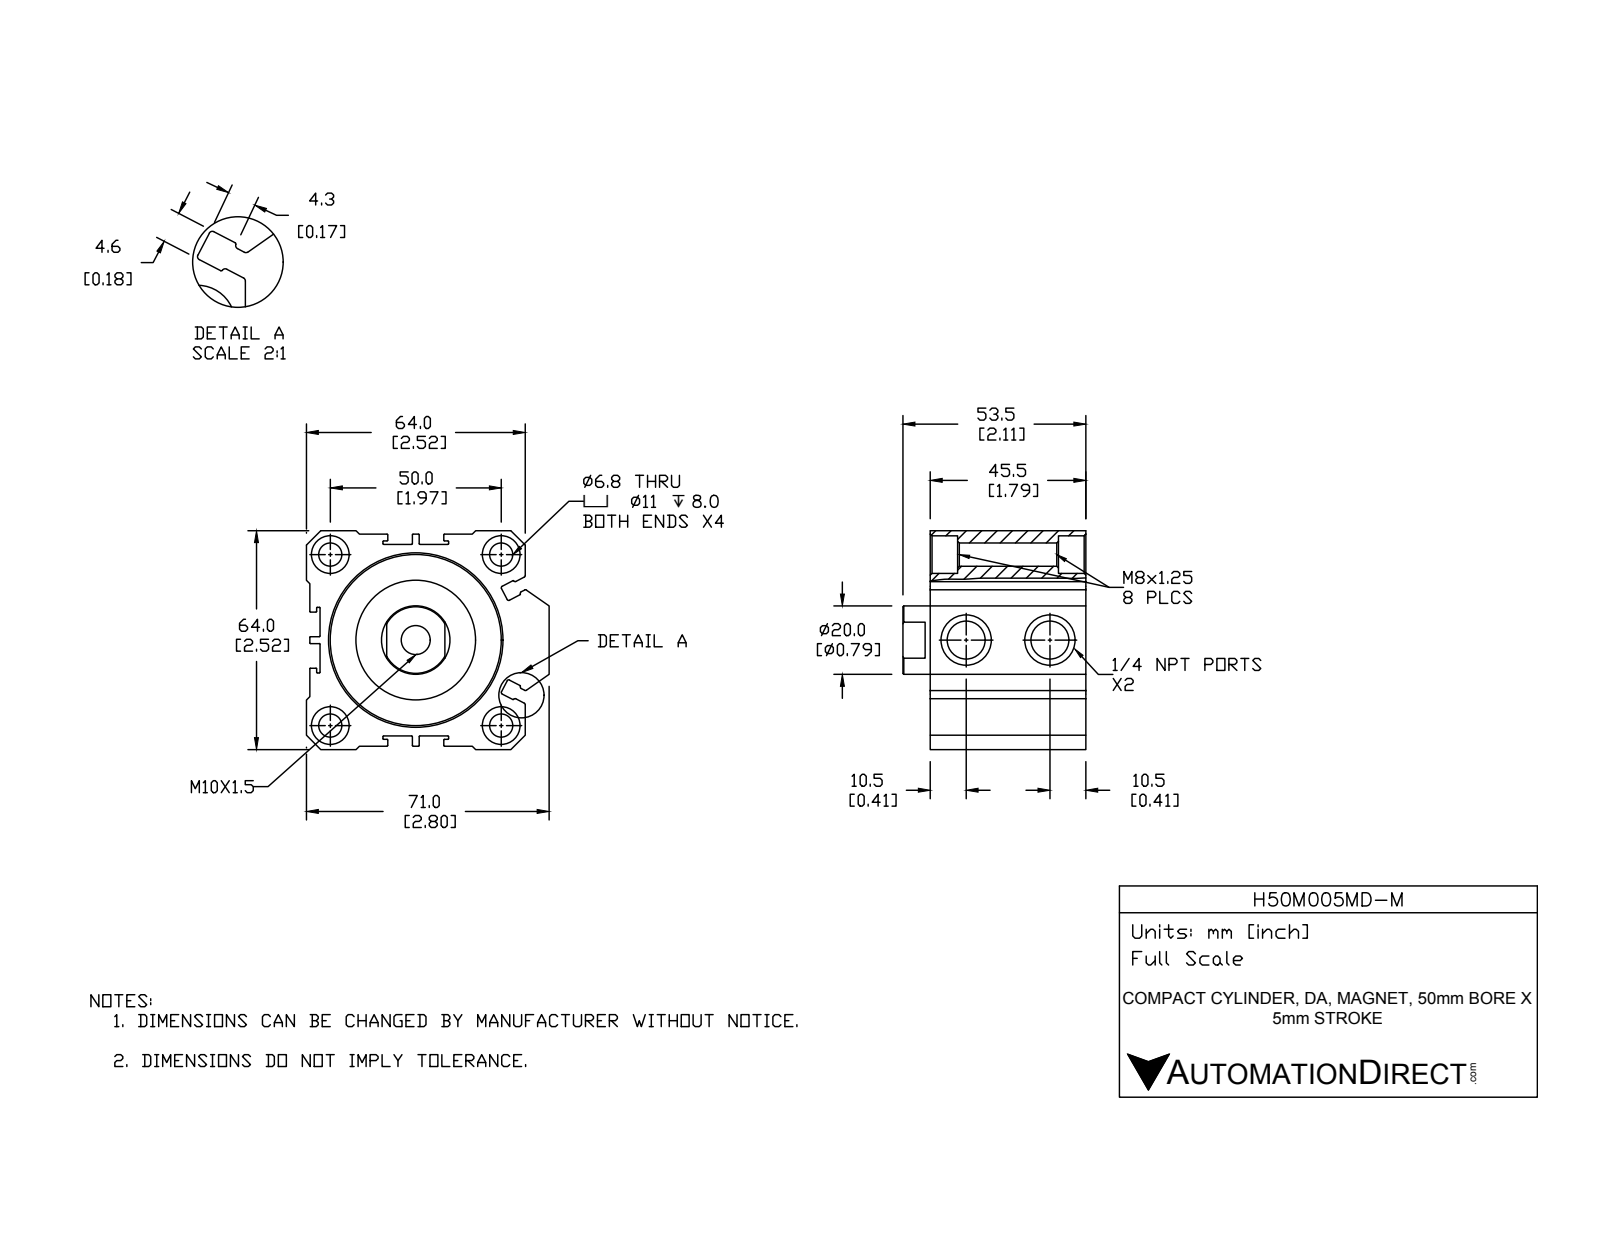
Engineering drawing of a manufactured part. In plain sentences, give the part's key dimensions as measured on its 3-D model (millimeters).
The part is named "H50M005MD-M; H50M005MD-M-PISTON; H50M005MD-M-BODY". Its 3-D file was written by "SolidWorks 2015 (CONFIG_CONTROL_DESIGN)". It is 2 solids with 255 faces: 99 planar, 103 cylindrical and 53 other. Overall it measures 71 by 64 by 53.5 millimeters. Its volume is 147 011 cubic millimeters and its surface area 47 246 square millimeters. Round holes: 4 of diameter 6.8, 4 of diameter 11, 2 of diameter 11.13, 1 of diameter 8.5, 1 of diameter 20, 1 of diameter 36, 1 of diameter 50. Round bosses or shafts: 1 of diameter 35, 1 of diameter 31. Partial cylindrical surfaces (rounded edges, fillets, slot ends): 40 of radius 0.2, 12 of radius 0.5. The main face-to-face distances are 4, 1, 3, 63, 60, 30, 33, 7, 2, 1.5. The hole center spacings are 35.36, 50, 70.71, 24.5.
